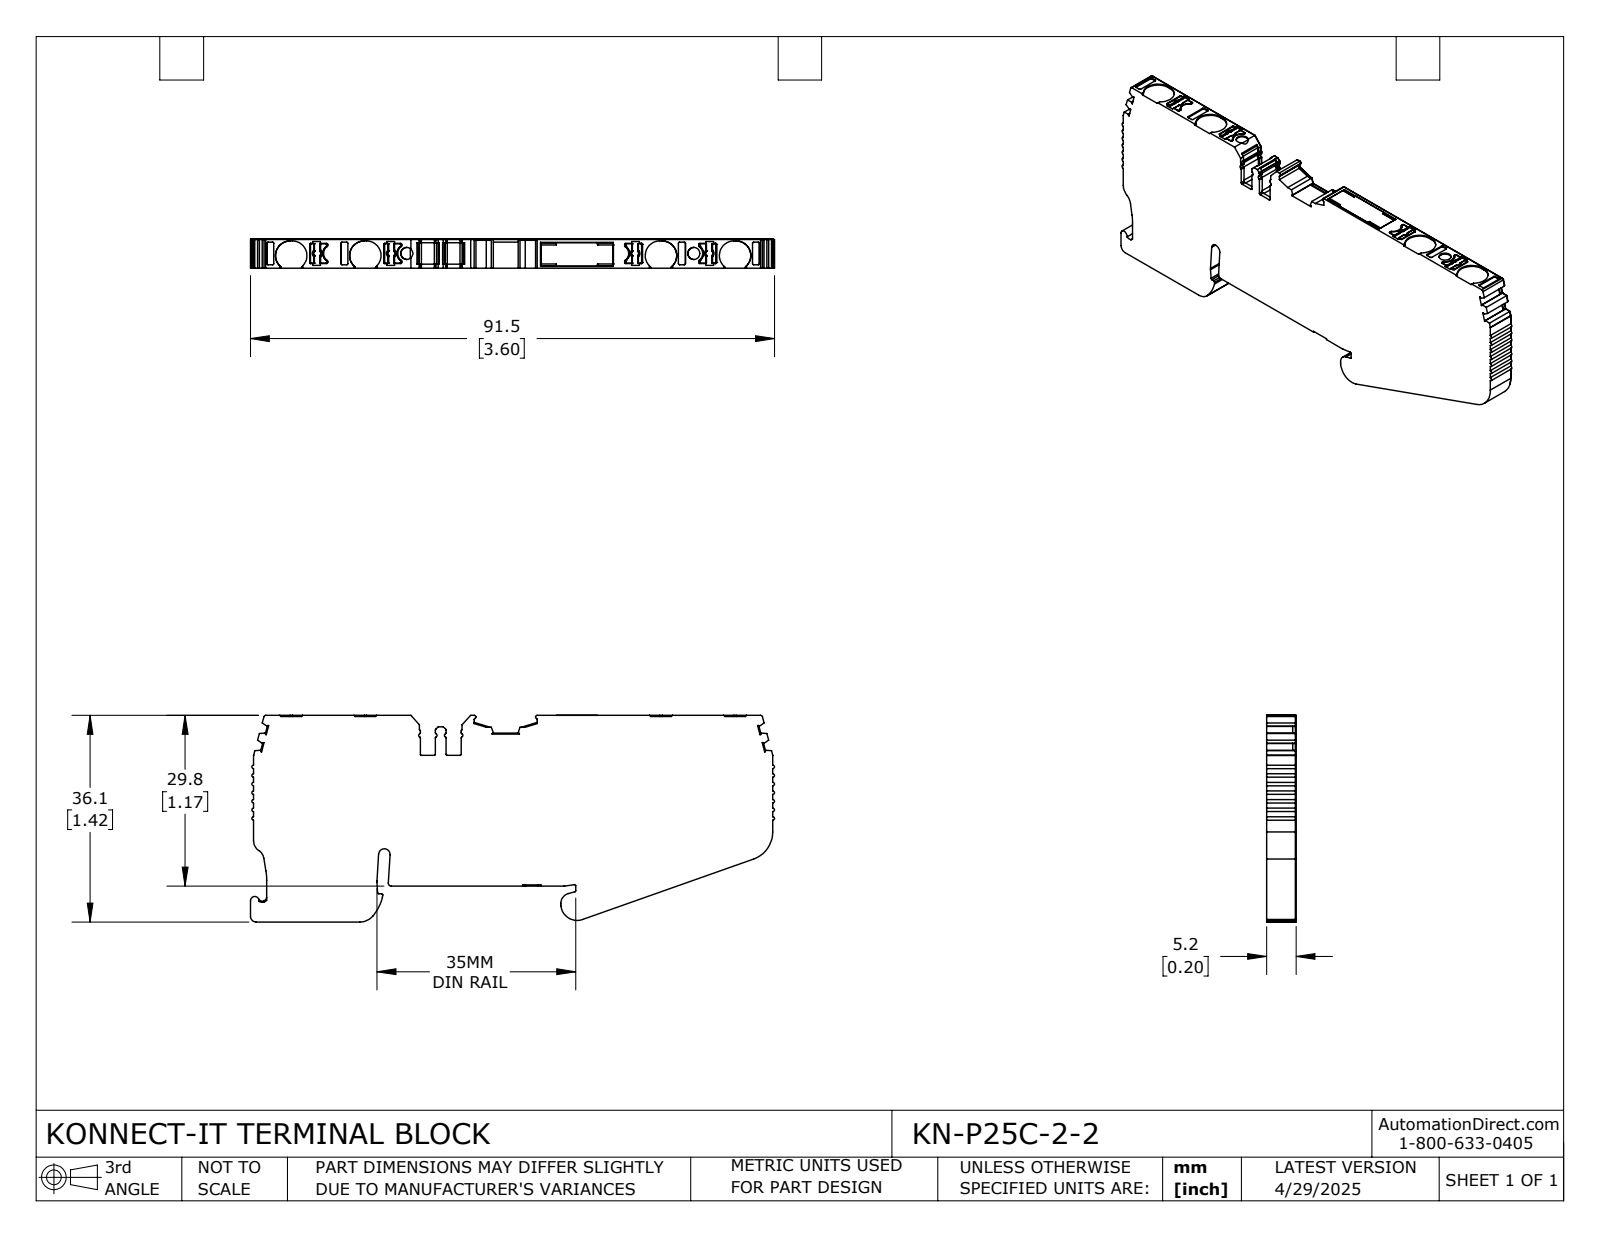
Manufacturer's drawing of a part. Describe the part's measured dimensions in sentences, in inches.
The part is named "KN-P25C-2-2". Its 3-D file was written by "SolidWorks 2024 (CONFIG_CONTROL_DESIGN)". It is 1 solid with 761 faces: 399 planar, 291 cylindrical and 71 other. Overall it measures 3.602 by 1.42 by 0.203 inches. Its volume is 0.855 cubic inches and its surface area 11.09 square inches. Round holes: 2 of diameter 0.083. Partial cylindrical surfaces (rounded edges, fillets, slot ends): 78 of radius 0.008, 39 of radius 0.012, 21 of radius 0.004, 18 of radius 0.02, 16 of radius 0.006, 9 of radius 0.016, 8 of radius 0.1, 4 of radius 0.059. The main face-to-face distances are 0.203, 1.166, 1.174, 0.246, 1.412, 1.42, 3.569, 0.197, 0.177, 0.047. The hole center spacings are 1.973.
